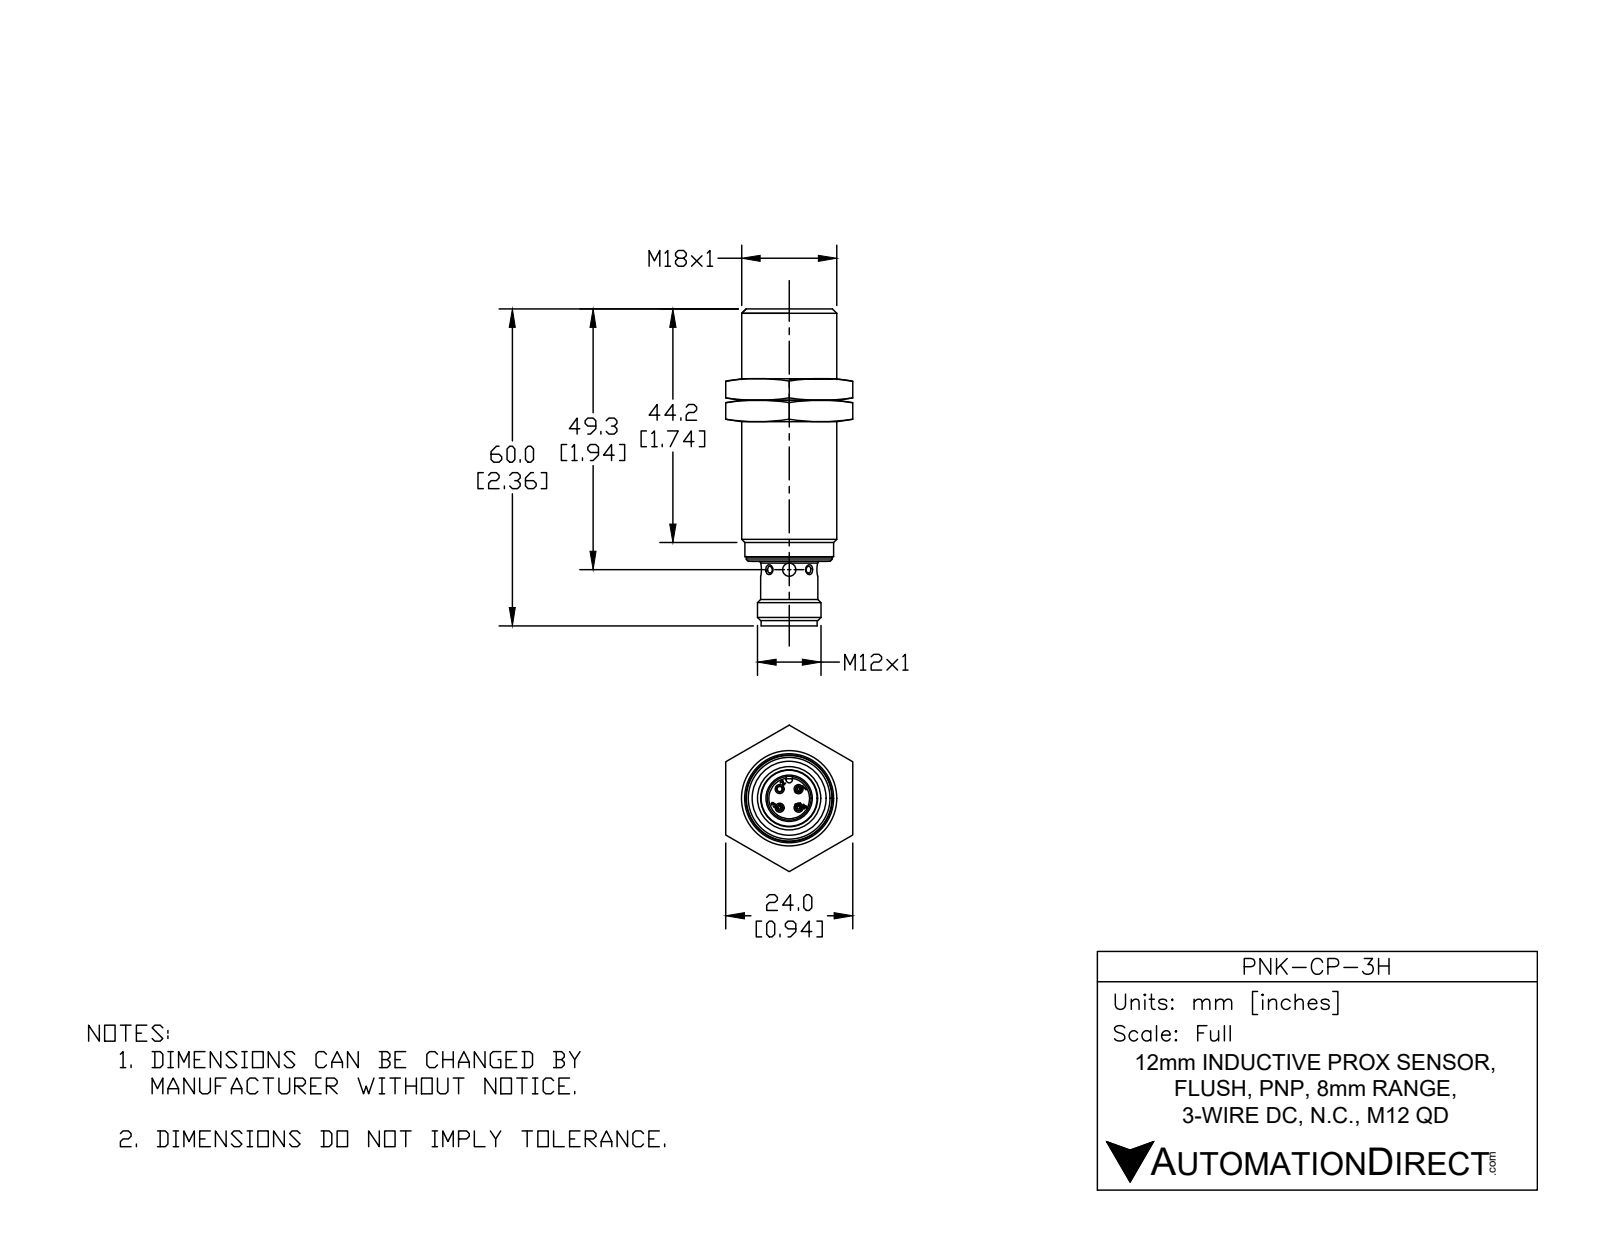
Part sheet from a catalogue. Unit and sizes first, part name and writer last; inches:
Units: inches
Overall size (bounding box): 2.362 × 0.709 × 0.709
Round holes (diameter × count): ⌀0.043 ×3, ⌀0.04 ×2, ⌀0.098 ×2, ⌀0.038 ×1, ⌀0.04 ×1, ⌀0.327 ×1, ⌀0.394 ×1, ⌀0.618 ×1, ⌀0.634 ×1
Round bosses / shafts (diameter × count): ⌀0.039 ×9, ⌀0.709 ×1, ⌀0.654 ×1, ⌀0.638 ×1, ⌀0.633 ×1, ⌀0.616 ×1, ⌀0.608 ×1, ⌀0.599 ×1
Partial cylindrical surfaces — rounded edges, fillets, slot ends (radius × count): R0.004 ×38, R0.024 ×1, R0.031 ×1, R0.161 ×1
Main face-to-face distances: 0.039, 0.022, 0.018, 1.87, 1.882, 1.86, 1.843, 1.848, 1.831, 2.323
Hole centre spacings: 0.098, 0.139, 0.197
Volume: 0.746 in³ · Surface area: 14.66 in²
Bodies: 1 solid, 1142 faces (751 planar, 150 cylindrical, 241 other)
Part name (STEP PRODUCT): PNK-CP-3H
STEP written by: SolidWorks 2017 (AUTOMOTIVE_DESIGN)
